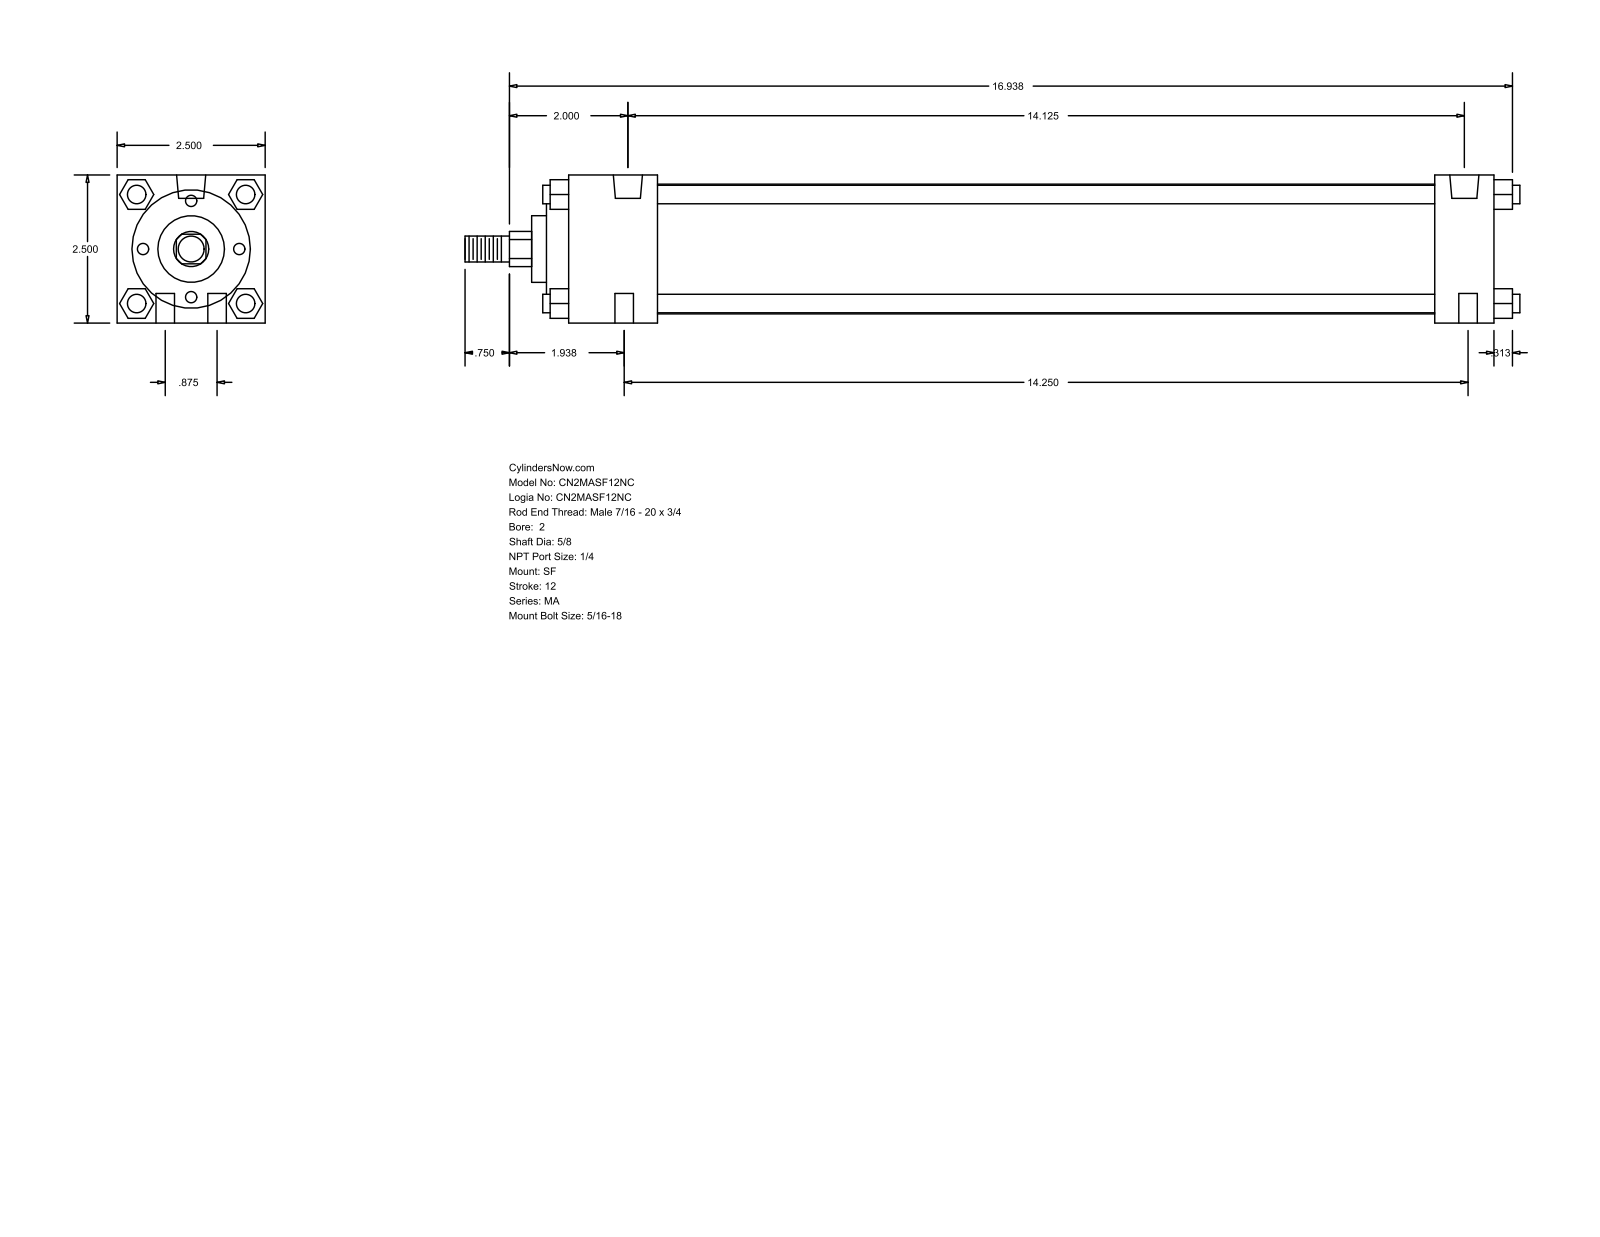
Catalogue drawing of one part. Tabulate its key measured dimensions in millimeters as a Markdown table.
| quantity | value |
| --- | --- |
| part name | MA_SF__0200_0.625 |
| STEP written by | GSSL Pune (CONFIG_CONTROL_DESIGN) |
| units | millimeters |
| bodies | 0 solids, 126 faces (95 planar, 31 cylindrical, 0 other) |
| overall size | 452.44 × 63.5 × 63.5 |
| round holes (diameter × count) | 7.94 × 6, 12.49 × 2 |
| round bosses / shafts (diameter × count) | 7.94 × 4, 55.63 × 1, 50.8 × 1, 28.57 × 1, 15.88 × 1, 11.11 × 1 |
| partial cylindrical surfaces (radius × count) | 7.54 × 1 |
| main face-to-face distances | 63.5, 12.7, 38.1, 396.87, 371.48, 25.39, 333.38, 358.77, 9.52, 47.62 |
| hole center spacings | 11.22, 360.53, 22.22, 358.77, 361.95, 362.63 |
